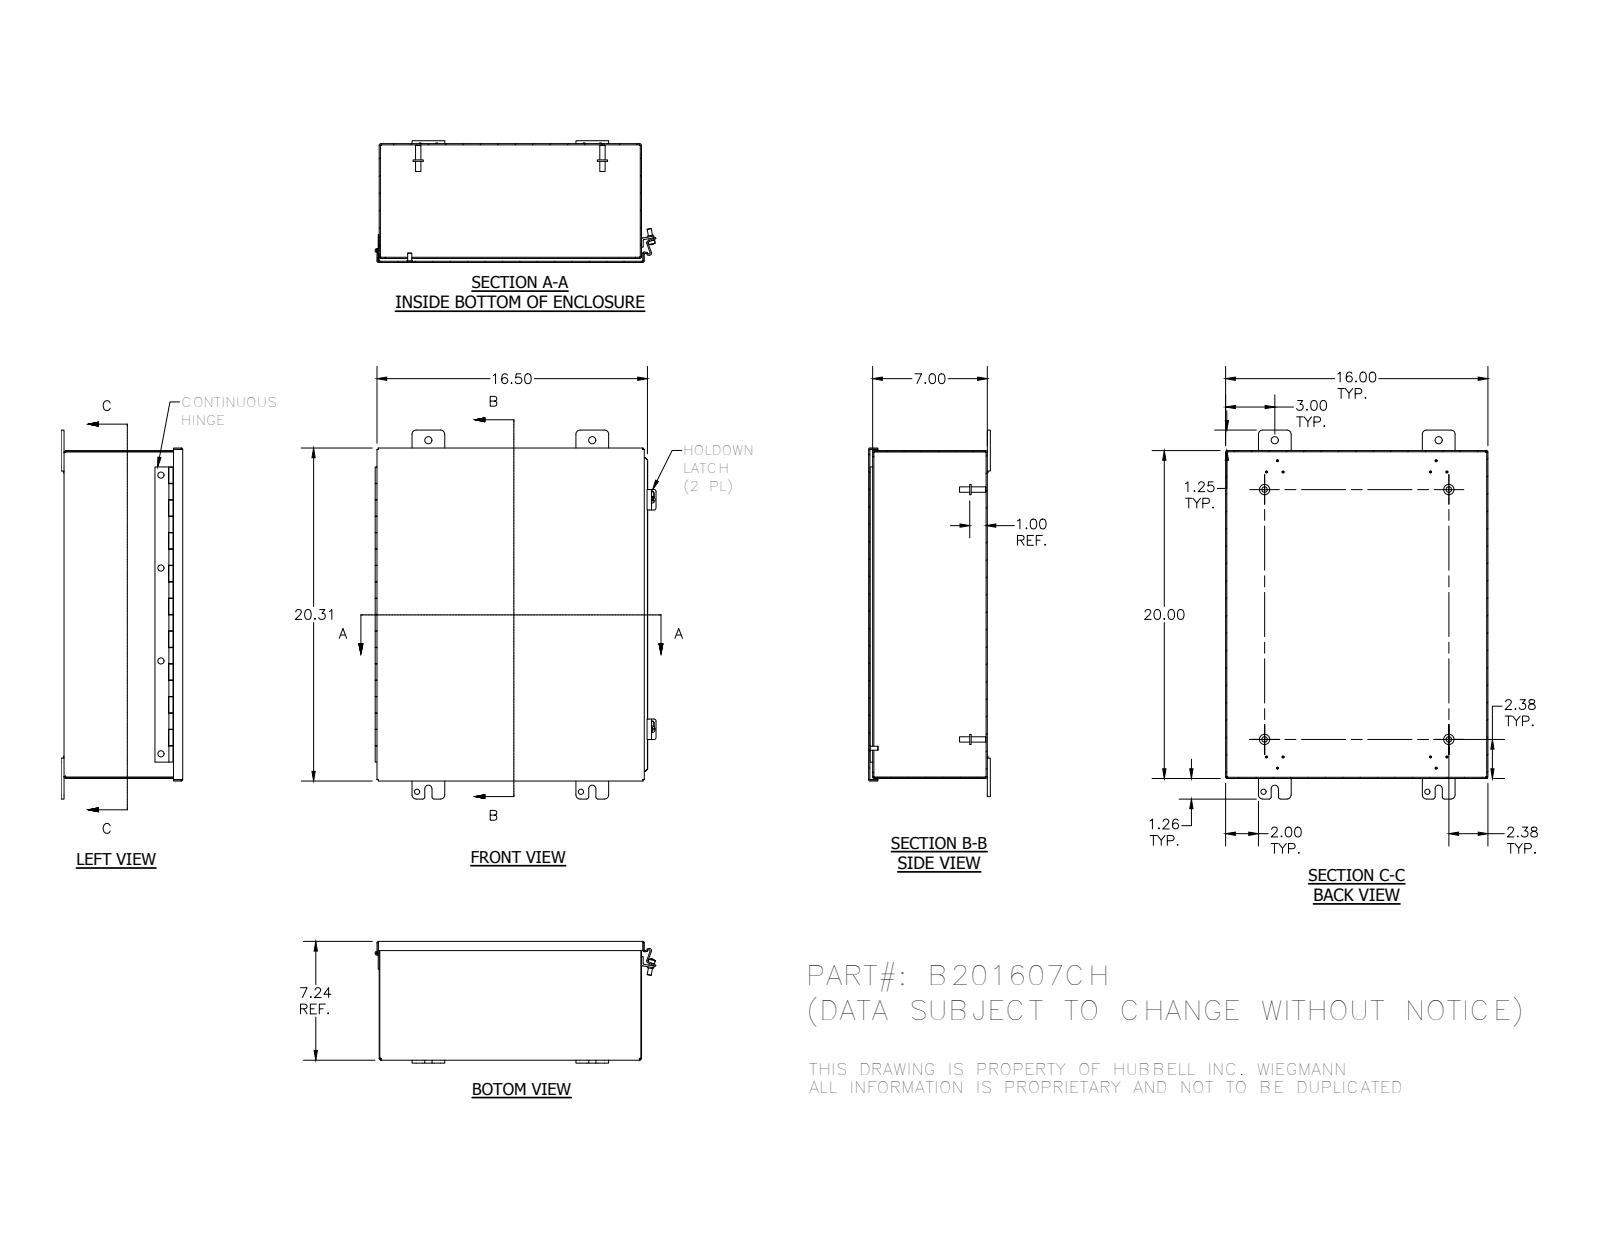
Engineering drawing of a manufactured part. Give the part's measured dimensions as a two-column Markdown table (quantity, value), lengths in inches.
| quantity | value |
| --- | --- |
| part name | B201607CH; B201607CHBKP; B2016CHLID; H6010100 (+8 more) |
| STEP written by | Autodesk Inventor 2012 (AUTOMOTIVE_DESIGN) |
| units | inches |
| bodies | 20 solids, 617 faces (371 planar, 177 cylindrical, 69 other) |
| overall size | 22.505 × 17.136 × 7.423 |
| volume | 95.79 in³ |
| surface area | 2 573 in² |
| round holes (diameter × count) | 0.11 × 4, 0.313 × 4, 0.375 × 4, 0.438 × 4, 0.196 × 2, 0.125 × 1, 0.125 × 1 |
| round bosses / shafts (diameter × count) | 0.625 × 4, 0.33 × 4, 0.25 × 4, 0.41 × 2, 0.344 × 2, 0.337 × 1, 0.12 × 1 |
| partial cylindrical surfaces (radius × count) | 0.125 × 16, 0.25 × 16, 0.031 × 8, 0.063 × 8, 0.07 × 8, 0.105 × 8, 0.016 × 5, 0.09 × 5 |
| main face-to-face distances | 0.074, 7.169, 7.243, 7.095, 15.926, 19.926, 16, 15.852, 20, 19.852 |
| hole center spacings | 1.593, 10, 20.005, 22.365, 0.75, 5.667, 9.423, 10.783 |
